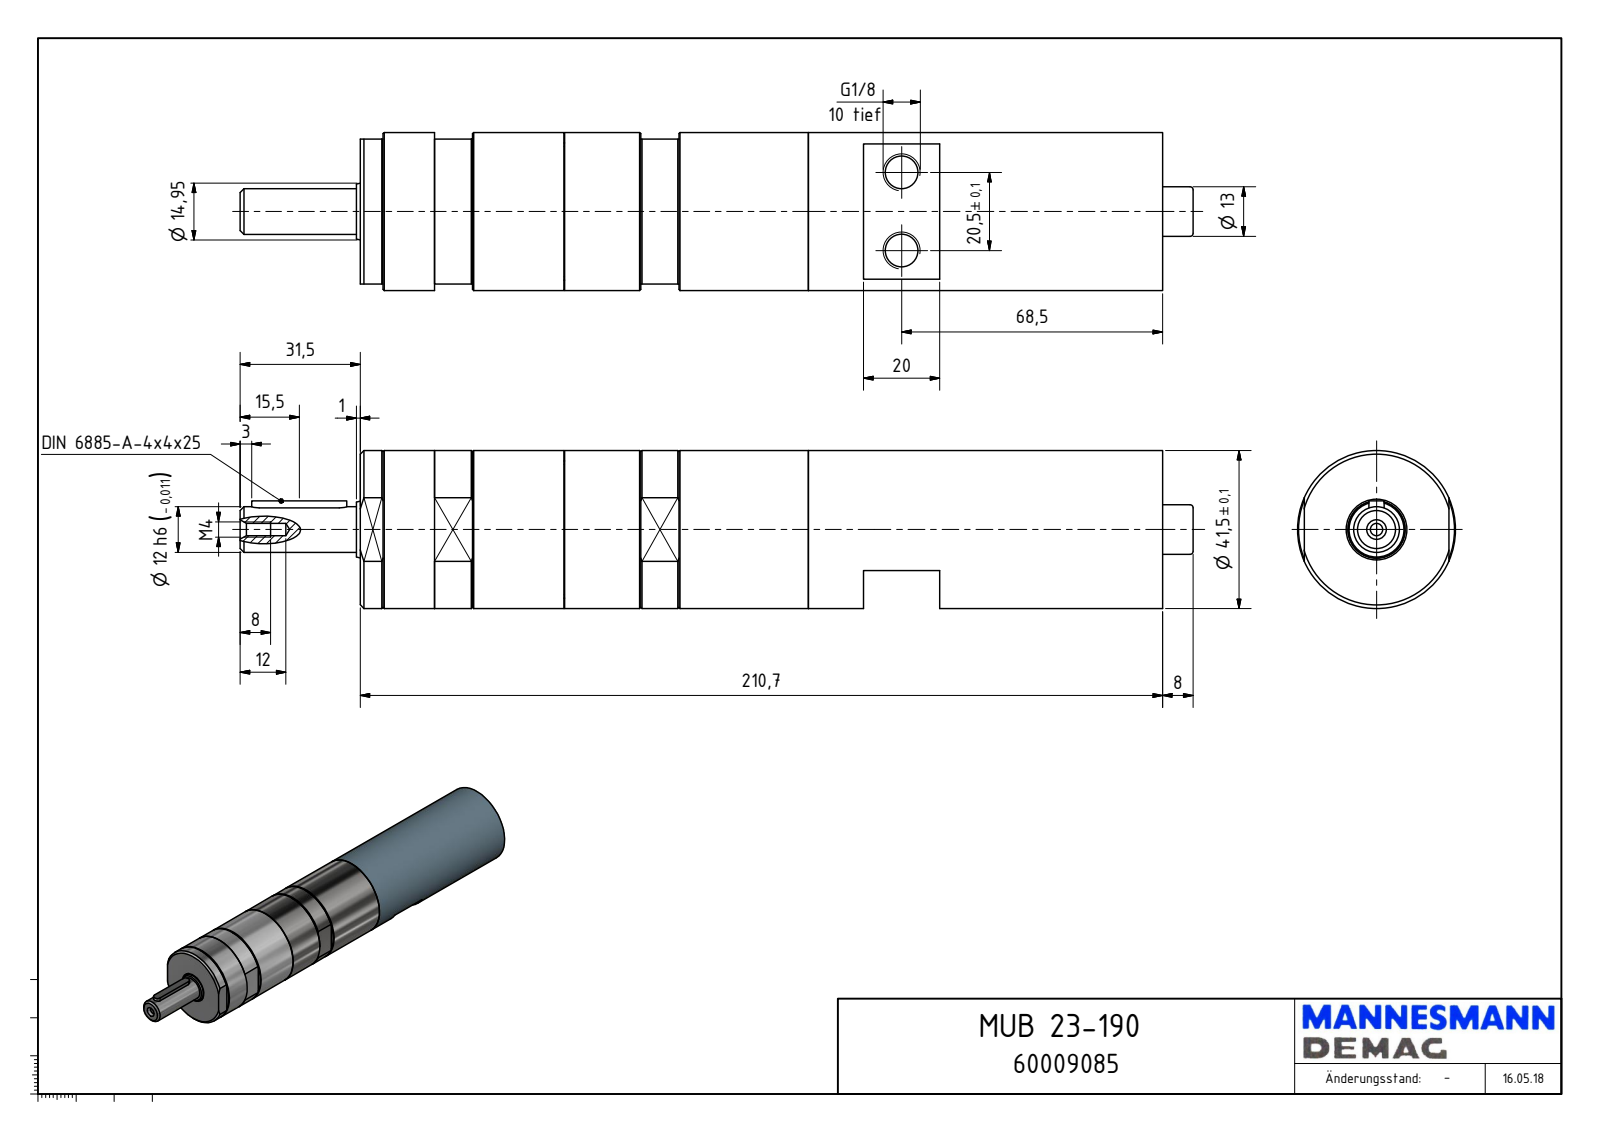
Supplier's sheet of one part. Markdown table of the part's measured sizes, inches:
| quantity | value |
| --- | --- |
| part name | MUB 23-190_60009085 |
| STEP written by | Autodesk Inventor 2018 (AUTOMOTIVE_DESIGN) |
| units | inches |
| bodies | 1 solid, 130 faces (62 planar, 45 cylindrical, 23 other) |
| overall size | 9.85 × 1.634 × 1.634 |
| volume | 17.17 in³ |
| surface area | 55.19 in² |
| round holes (diameter × count) | 0.079 × 2, 0.337 × 2, 0.128 × 1, 0.335 × 1, 0.512 × 1, 0.63 × 1, 1.555 × 1 |
| round bosses / shafts (diameter × count) | 1.634 × 1, 1.535 × 1, 1.417 × 1, 0.589 × 1, 0.472 × 1, 0.315 × 1 |
| partial cylindrical surfaces (radius × count) | 0.079 × 4, 0.063 × 2, 0.098 × 2, 0.319 × 1, 0.482 × 1 |
| main face-to-face distances | 8.295, 3.091, 1.496, 2.106, 6.189, 2.114, 6.181, 2.303, 0.787, 5.992 |
| hole center spacings | 0.509, 0.807, 0.984 |
